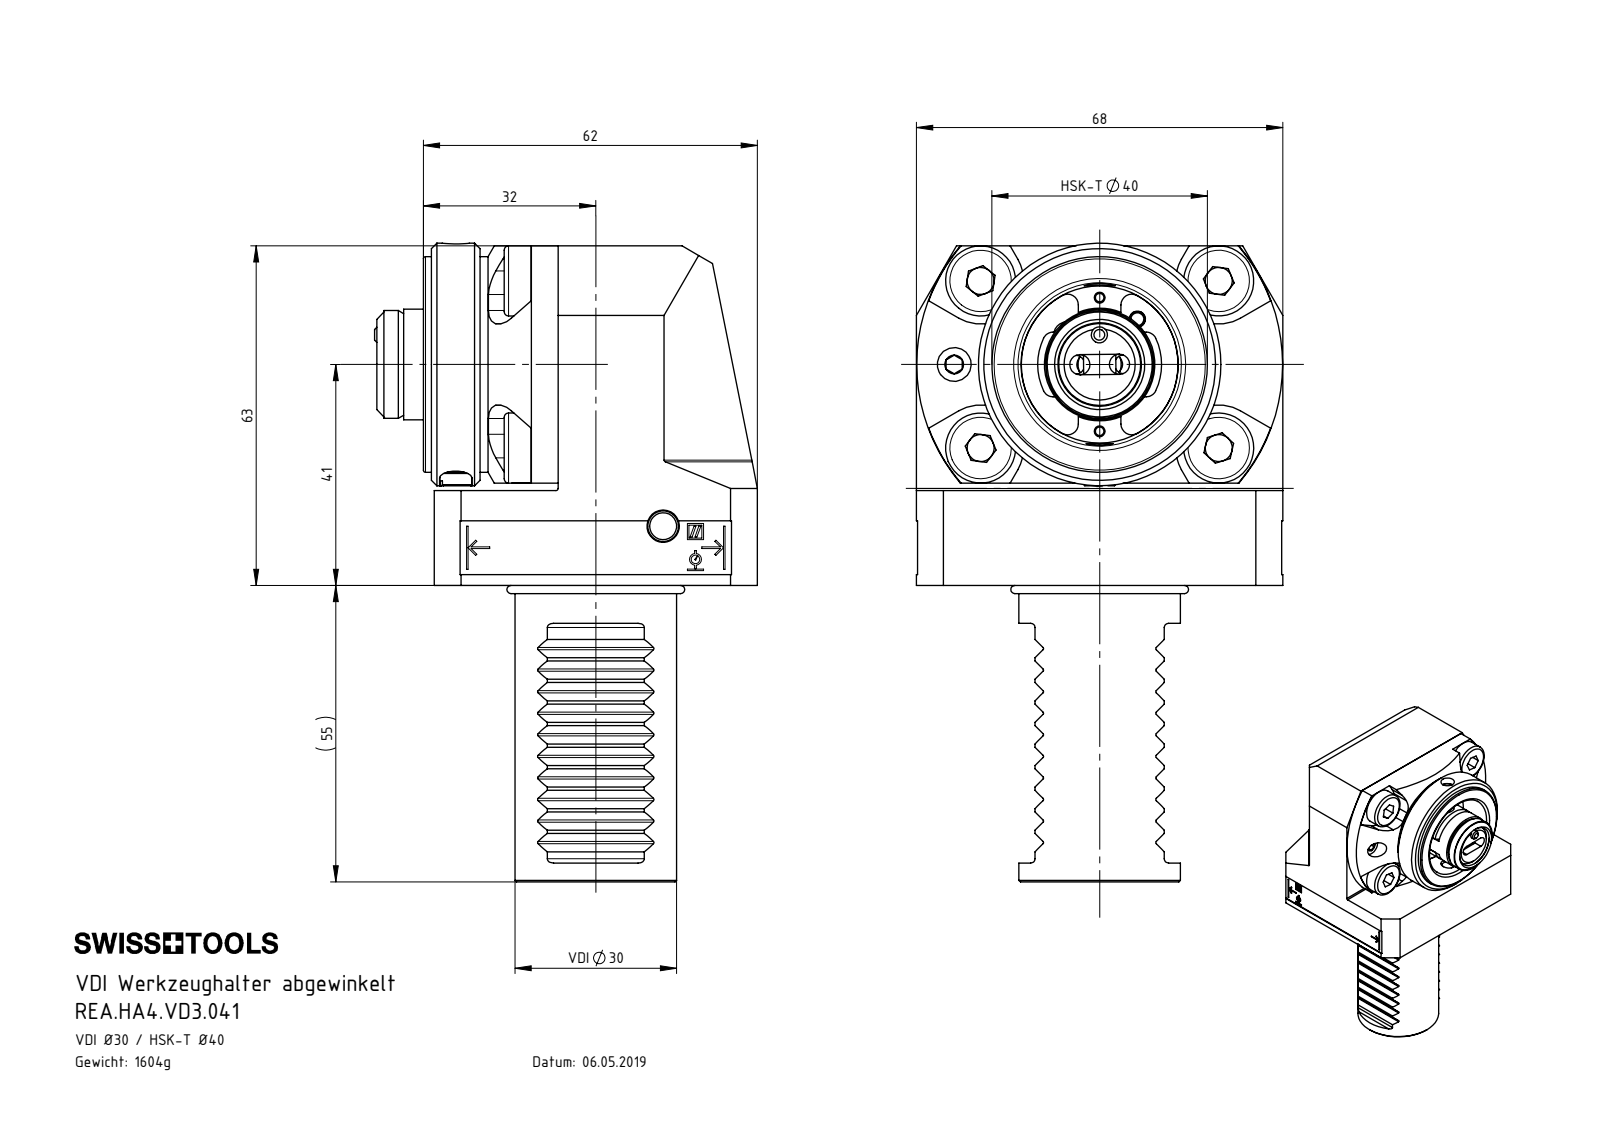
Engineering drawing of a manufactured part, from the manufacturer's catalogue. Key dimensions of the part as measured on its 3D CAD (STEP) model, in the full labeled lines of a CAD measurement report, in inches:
Part name (STEP PRODUCT): DIN 7984 - M8 x 16; HA4-ER1.001.000; HA4-ER3.003.009; ISO 8734 - 5 x 12_PreviewCfg (+8 more)
STEP written by: SolidWorks 2022 (AUTOMOTIVE_DESIGN)
Units: inches
Bodies: 30 solids, 932 faces (329 planar, 291 cylindrical, 312 other)
Overall size (bounding box): 4.665 × 2.797 × 2.677
Volume: 13.61 in³ · Surface area: 117.1 in²
Round holes (diameter × count): ⌀0.197 ×7, ⌀0.268 ×4, ⌀0.354 ×4, ⌀0.512 ×3, ⌀0.063 ×2, ⌀0.118 ×2, ⌀0.138 ×2, ⌀0.148 ×2, ⌀0.236 ×2, ⌀0.094 ×1, ⌀0.098 ×1, ⌀0.165 ×1
Round bosses / shafts (diameter × count): ⌀0.512 ×4, ⌀0.315 ×4, ⌀0.236 ×4, ⌀1.772 ×1, ⌀1.575 ×1, ⌀1.555 ×1, ⌀1.443 ×1, ⌀0.807 ×1
Partial cylindrical surfaces — rounded edges, fillets, slot ends (radius × count): R0.012 ×20, R0.197 ×9, R0.039 ×8, R0.031 ×4, R0.077 ×4, R0.079 ×4, R0.315 ×4, R0.016 ×3
Main face-to-face distances: 2.362, 2.48, 1.787, 0.693, 0.787, 1.654, 0.111, 0.768, 0.197, 0.669
Hole centre spacings: 1.22, 2.126, 1.063, 0.879, 0.879, 0.947, 0.949, 1.063
